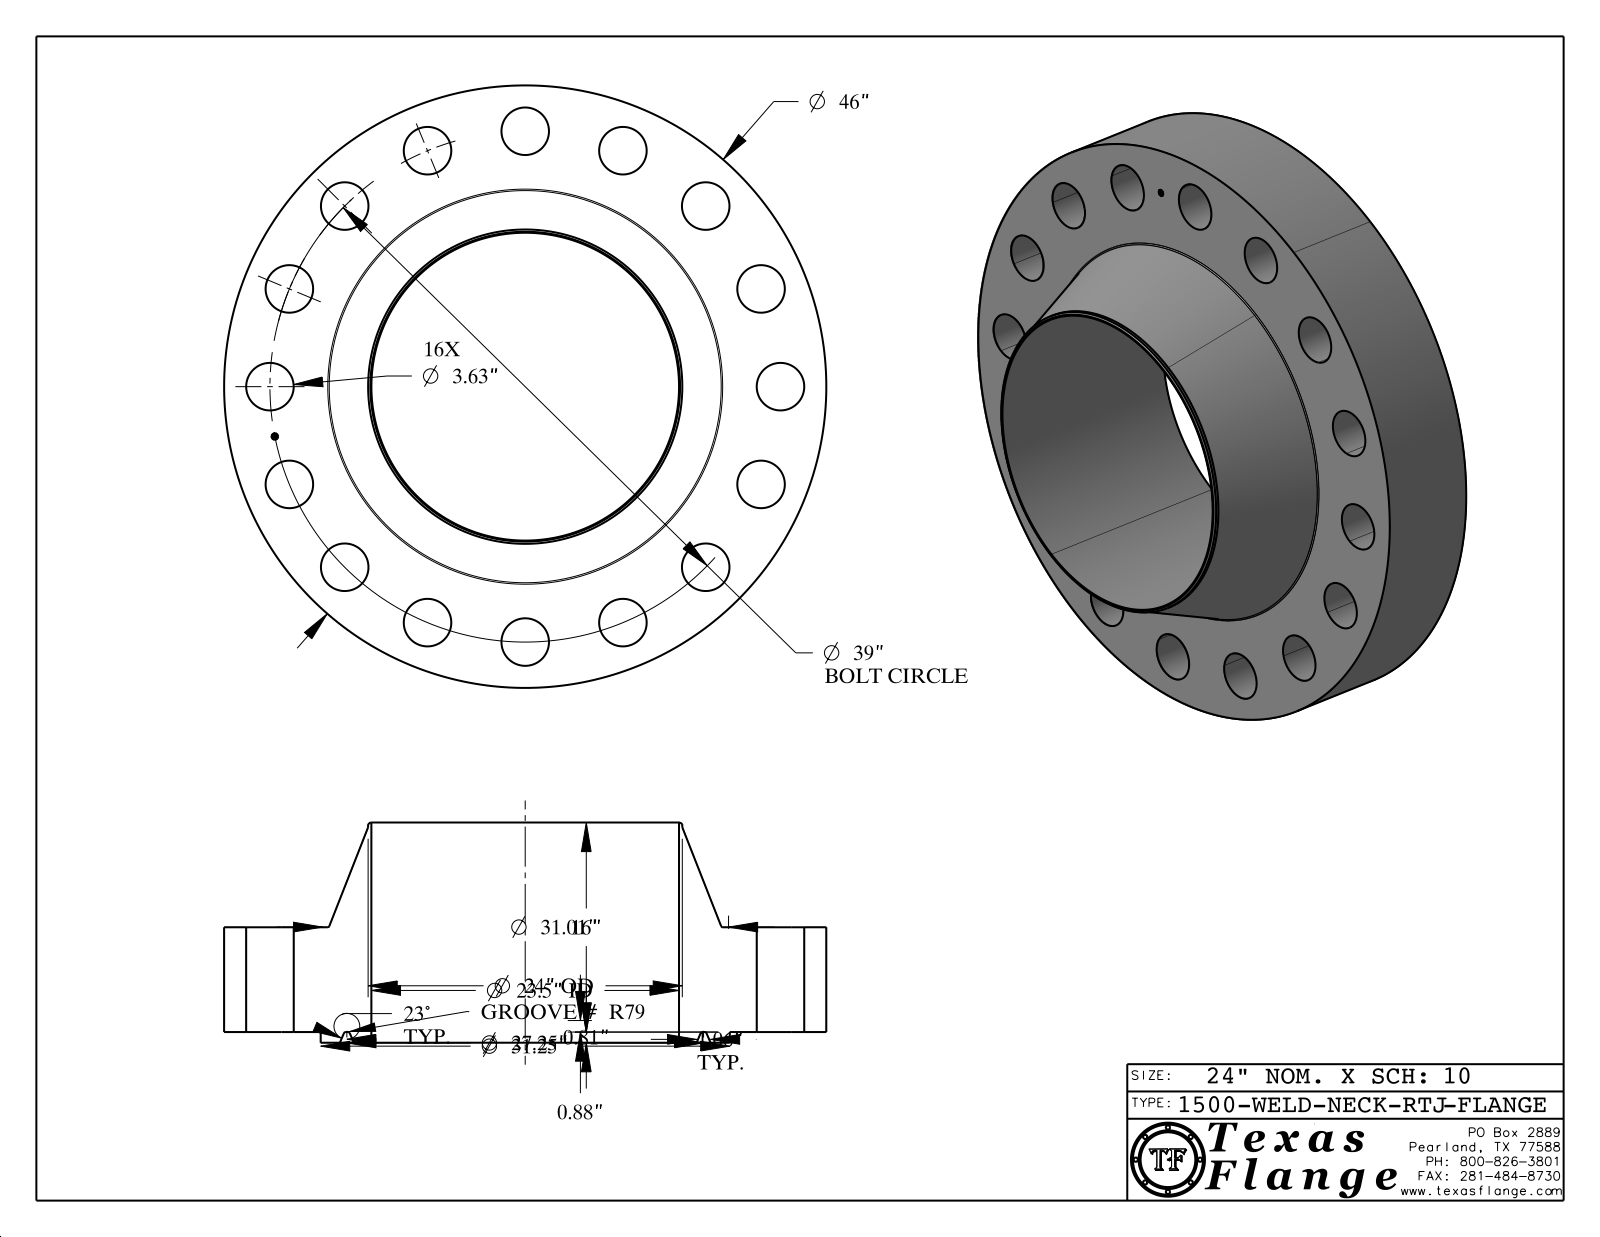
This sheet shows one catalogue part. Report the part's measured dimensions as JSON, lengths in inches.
{"part_name": "1500-WELD-NECK-RTJ", "step_written_by": "CATIA V5 STEP AP214 (AUTOMOTIVE_DESIGN)", "units": "inches", "bodies": {"solids": 1, "faces": 445, "planar": 371, "cylindrical": 60, "other": 14}, "overall_size": [46, 46, 16.813], "volume_in3": 9805, "surface_area_in2": 6612, "round_holes": [[3.63, 16], [0.495, 1], [23.5, 1]], "round_bosses_or_shafts": [[0.03, 8], [46, 1], [31.25, 1], [24, 1], [0.39, 1]], "face_to_face_distances": [8, 0.813, 8.813, 16.813, 16, 8.798, 7.985, 0.015, 8.015, 0.148], "hole_center_spacings": [19.5, 21.667, 27.577, 38.251, 14.925, 36.031, 7.608, 7.609]}
